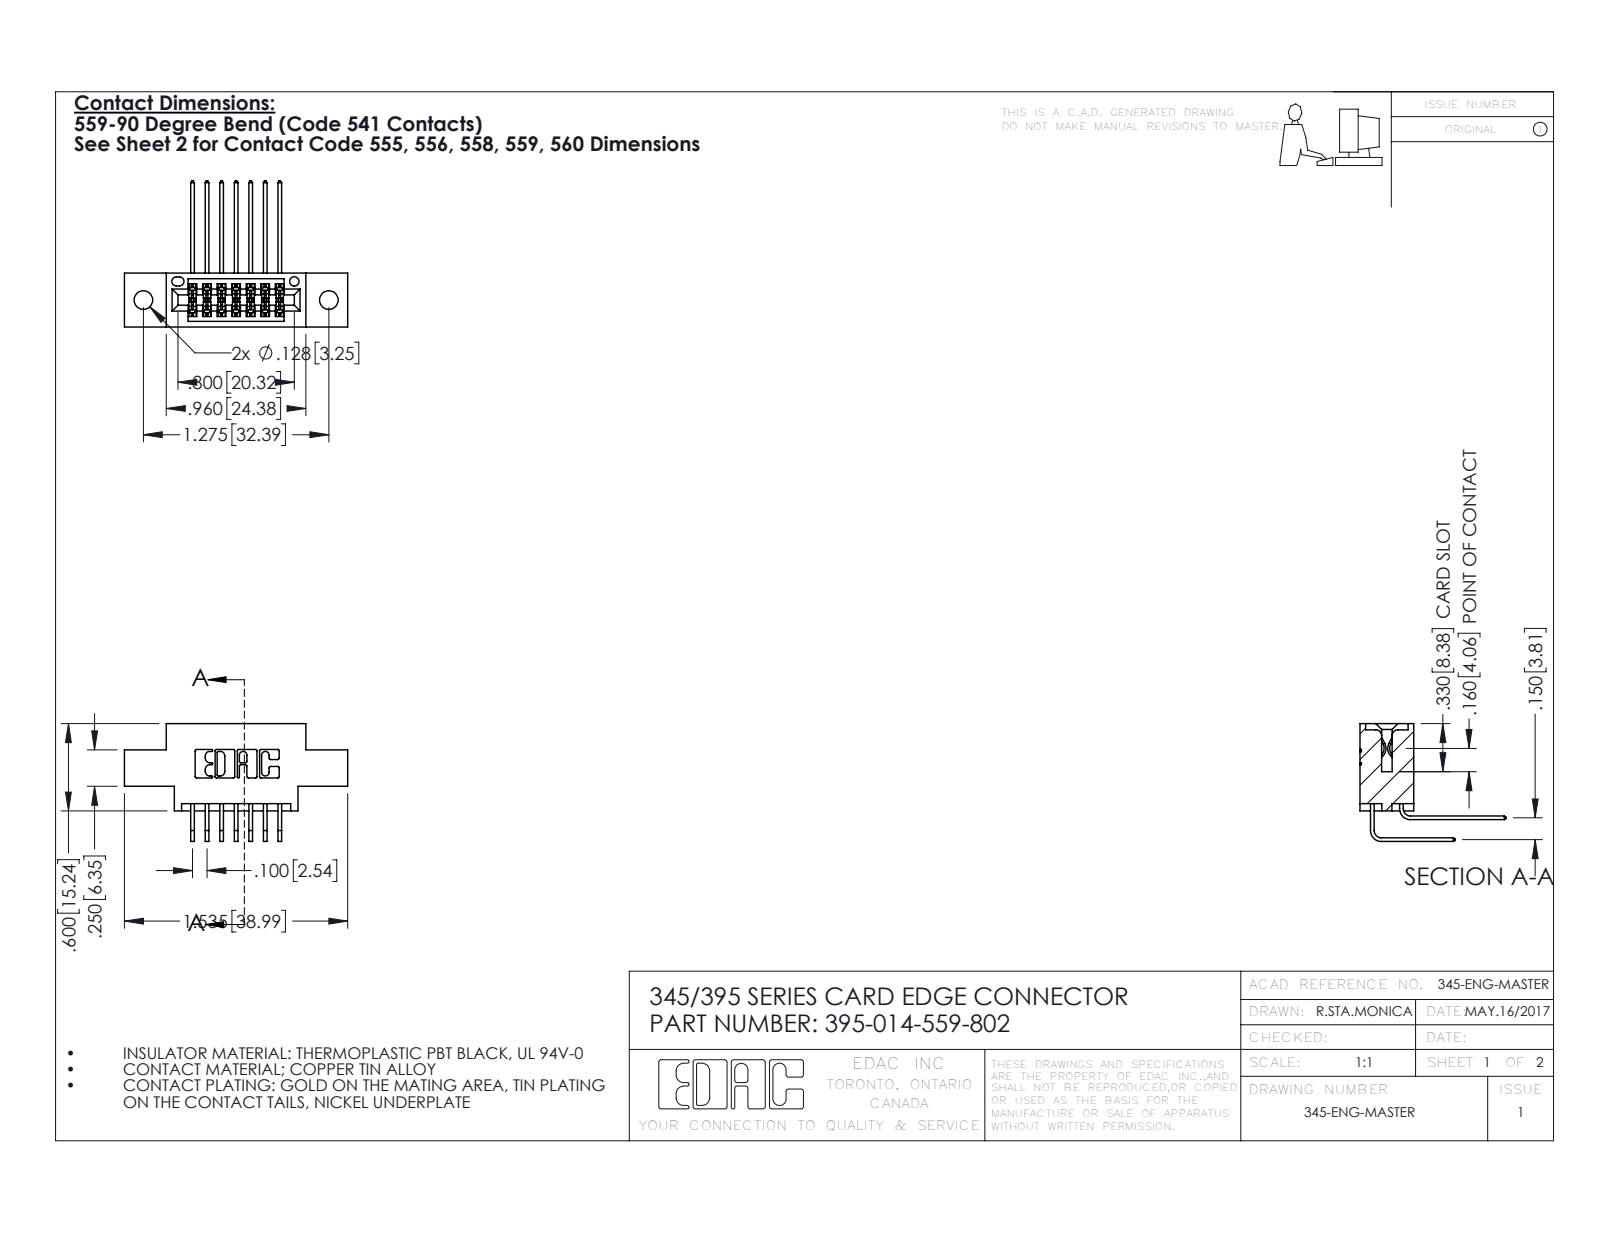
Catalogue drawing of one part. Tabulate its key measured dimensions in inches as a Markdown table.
| quantity | value |
| --- | --- |
| part name | 345-292-001_558 559 Tail - 1; 395-014-559-802; 345 Part_0.170 Offset - 0.128 Dia; 345-292-001_559 Tail - 2 |
| STEP written by | SolidWorks 2016 (CONFIG_CONTROL_DESIGN) |
| units | inches |
| bodies | 15 solids, 858 faces (574 planar, 284 cylindrical, 0 other) |
| overall size | 1.535 × 1.005 × 0.809 |
| volume | 0.207 in³ |
| surface area | 7.112 in² |
| round holes (diameter × count) | 0.128 × 2, 0.064 × 1 |
| partial cylindrical surfaces (radius × count) | 0.006 × 22, 0.01 × 22, 0.007 × 6, 0.031 × 6, 0.026 × 3, 0.014 × 2, 0.019 × 2, 0.022 × 2 |
| main face-to-face distances | 0.2, 0.37, 0.072, 0.298, 0.1, 0.15, 0.098, 0.272, 0.025, 0.3 |
| hole center spacings | 0.27, 1.045, 1.275 |
